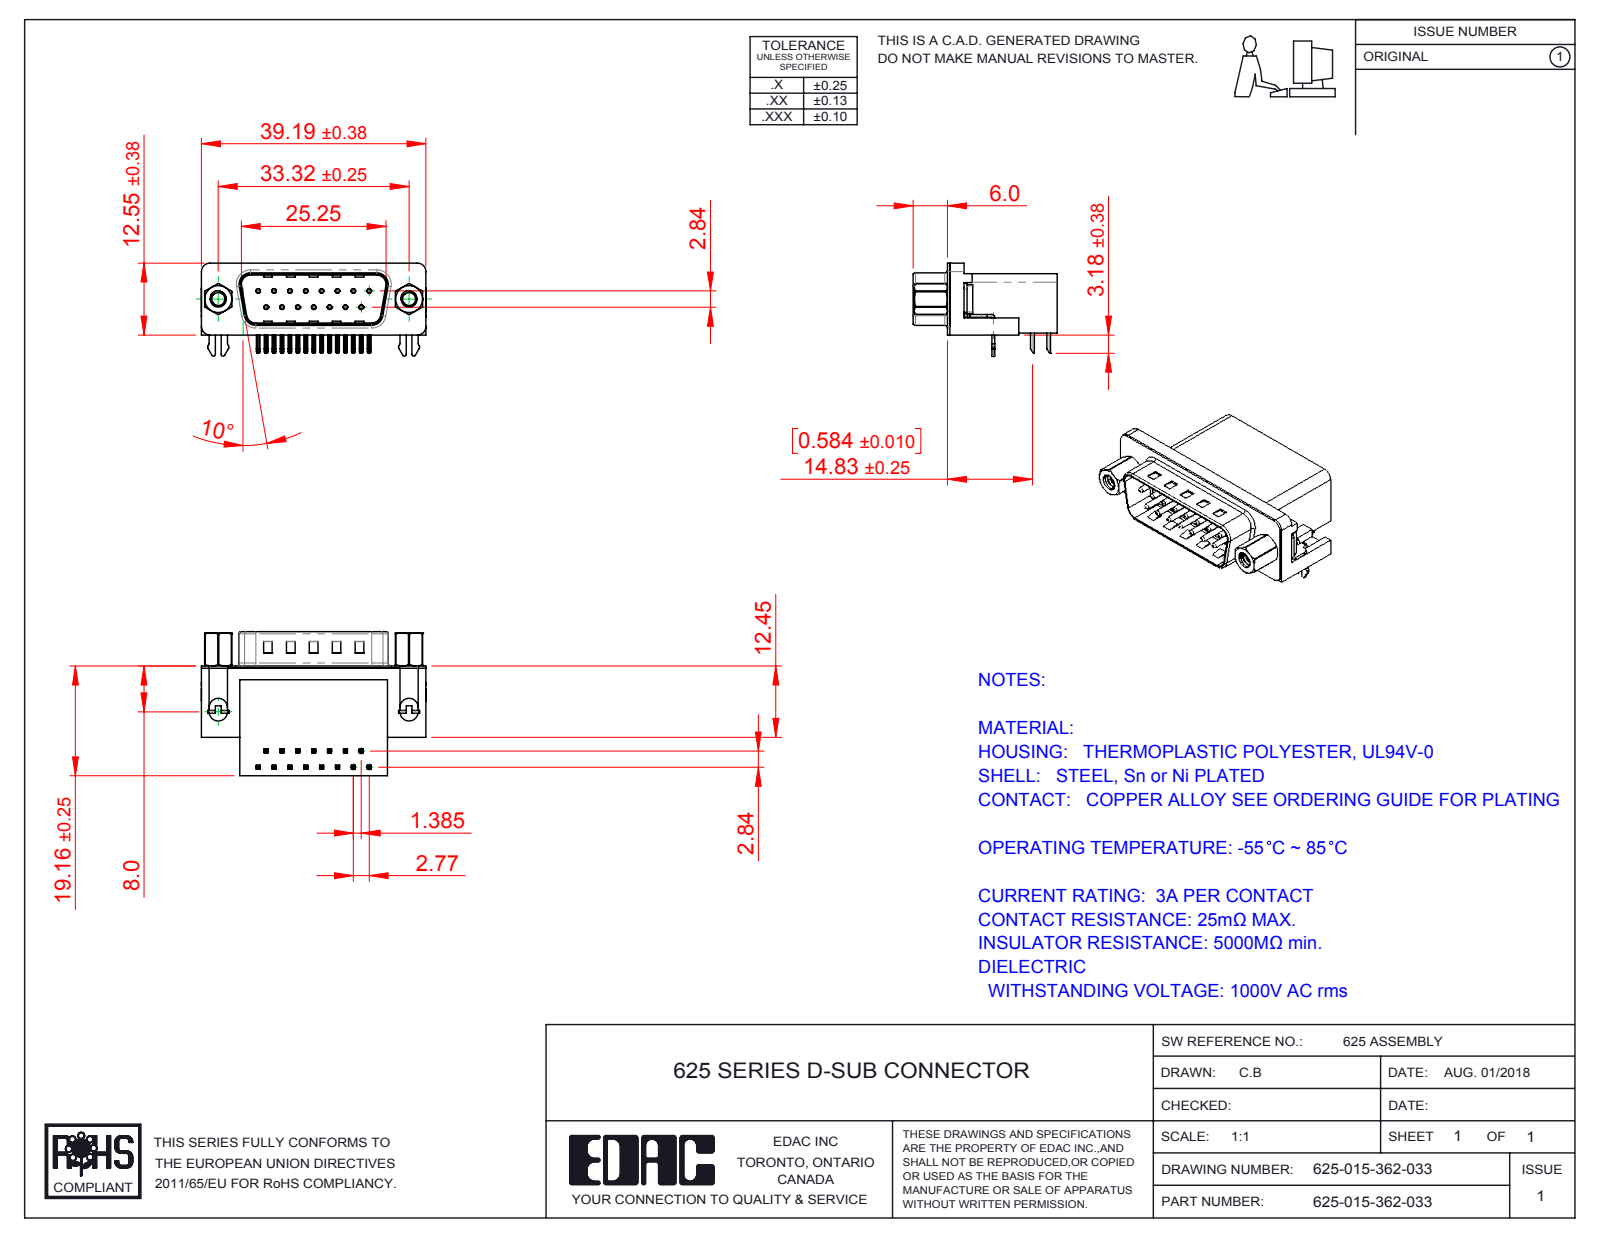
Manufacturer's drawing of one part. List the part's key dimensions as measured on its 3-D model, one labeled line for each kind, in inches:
Part name (STEP PRODUCT): 625 4-40 Threaded Rivet; 625 Housing_15 Socket; 625 4-40 Hex Standoff 5; 625 Contact Top (+4 more)
STEP written by: SolidWorks 2016 (CONFIG_CONTROL_DESIGN)
Units: inches
Bodies: 23 solids, 1645 faces (947 planar, 527 cylindrical, 171 other)
Overall size (bounding box): 1.544 × 0.991 × 0.64
Volume: 0.394 in³ · Surface area: 10.72 in²
Round holes (diameter × count): ⌀0.014 ×15, ⌀0.031 ×15, ⌀0.089 ×2, ⌀0.09 ×2, ⌀0.157 ×2, ⌀0.189 ×2, ⌀0.197 ×2
Round bosses / shafts (diameter × count): ⌀0.03 ×15, ⌀0.193 ×2, ⌀0.187 ×2, ⌀0.154 ×2, ⌀0.11 ×2
Partial cylindrical surfaces — rounded edges, fillets, slot ends (radius × count): R0.01 ×68, R0.005 ×30, R0.039 ×16, R0.02 ×14, R0.063 ×8, R0.059 ×6, R0.013 ×4, R0.035 ×4
Main face-to-face distances: 0.016, 0.407, 0.739, 0.083, 0.754, 0.412, 0.067, 0.428, 0.345, 0.64
Hole centre spacings: 0.124, 0.109, 0.218, 0.327, 0.436, 0.198, 0.198, 0.294
